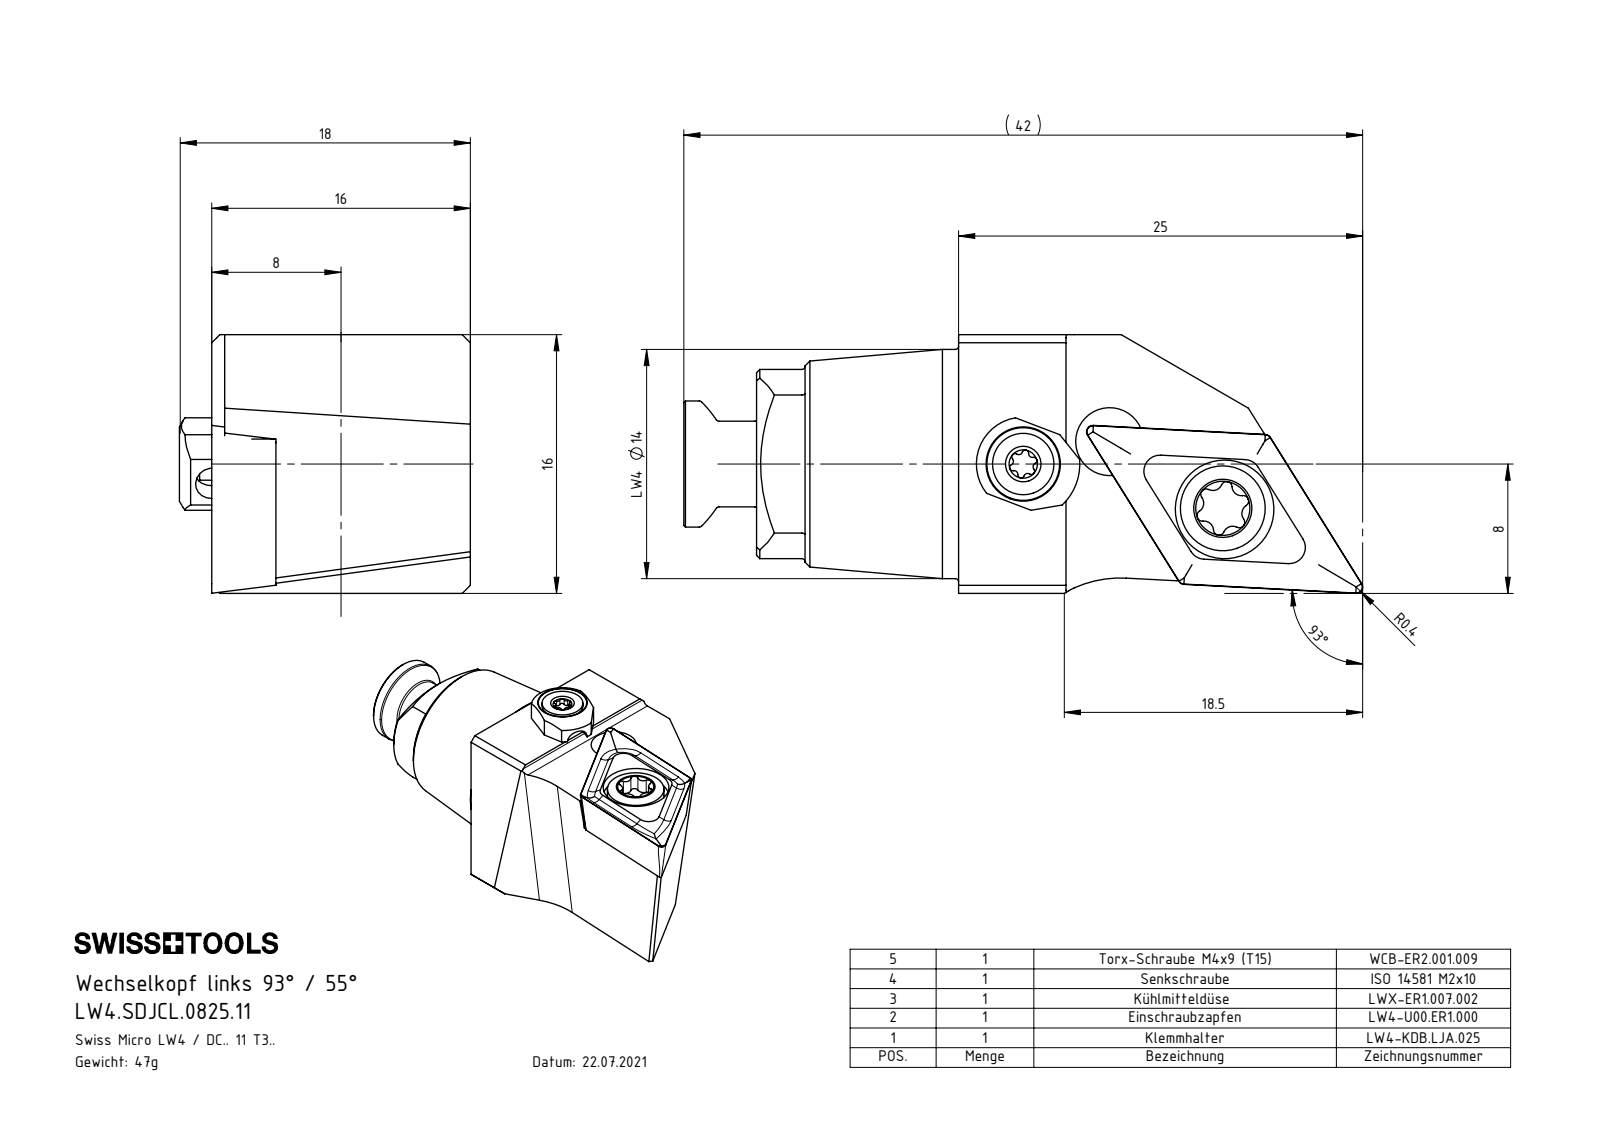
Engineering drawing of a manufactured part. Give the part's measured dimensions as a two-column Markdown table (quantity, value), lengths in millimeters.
| quantity | value |
| --- | --- |
| part name | WCB-ER2.001.009_A; LW4-KDB.LJA.025_A; ISO 14581 - M2x10; LW4.SDJCL.0825.11 (+3 more) |
| STEP written by | SolidWorks 2022 (CONFIG_CONTROL_DESIGN) |
| units | millimeters |
| bodies | 6 solids, 262 faces (70 planar, 81 cylindrical, 111 other) |
| overall size | 42.01 × 18 × 16 |
| volume | 5 759 mm³ |
| surface area | 3 690 mm² |
| round holes (diameter × count) | 2 × 2, 1.6 × 1, 2.5 × 1, 3 × 1, 3.3 × 1, 4.2 × 1, 4.4 × 1, 5.5 × 1, 6.1 × 1 |
| round bosses / shafts (diameter × count) | 14.17 × 1, 7.7 × 1, 6 × 1, 5.3 × 1, 5.25 × 1, 5 × 1, 4 × 1, 3.8 × 1 |
| partial cylindrical surfaces (radius × count) | 0.2 × 8, 0.24 × 6, 0.34 × 6, 0.59 × 6, 0.5 × 1, 1 × 1, 2.9 × 1, 3.5 × 1 |
| main face-to-face distances | 16, 12.03, 3.97, 15.2, 3.17, 0.8, 7.5, 2, 3, 12.5 |
| hole center spacings | 6.14, 8.13, 8.25, 10.03, 10.13 |
